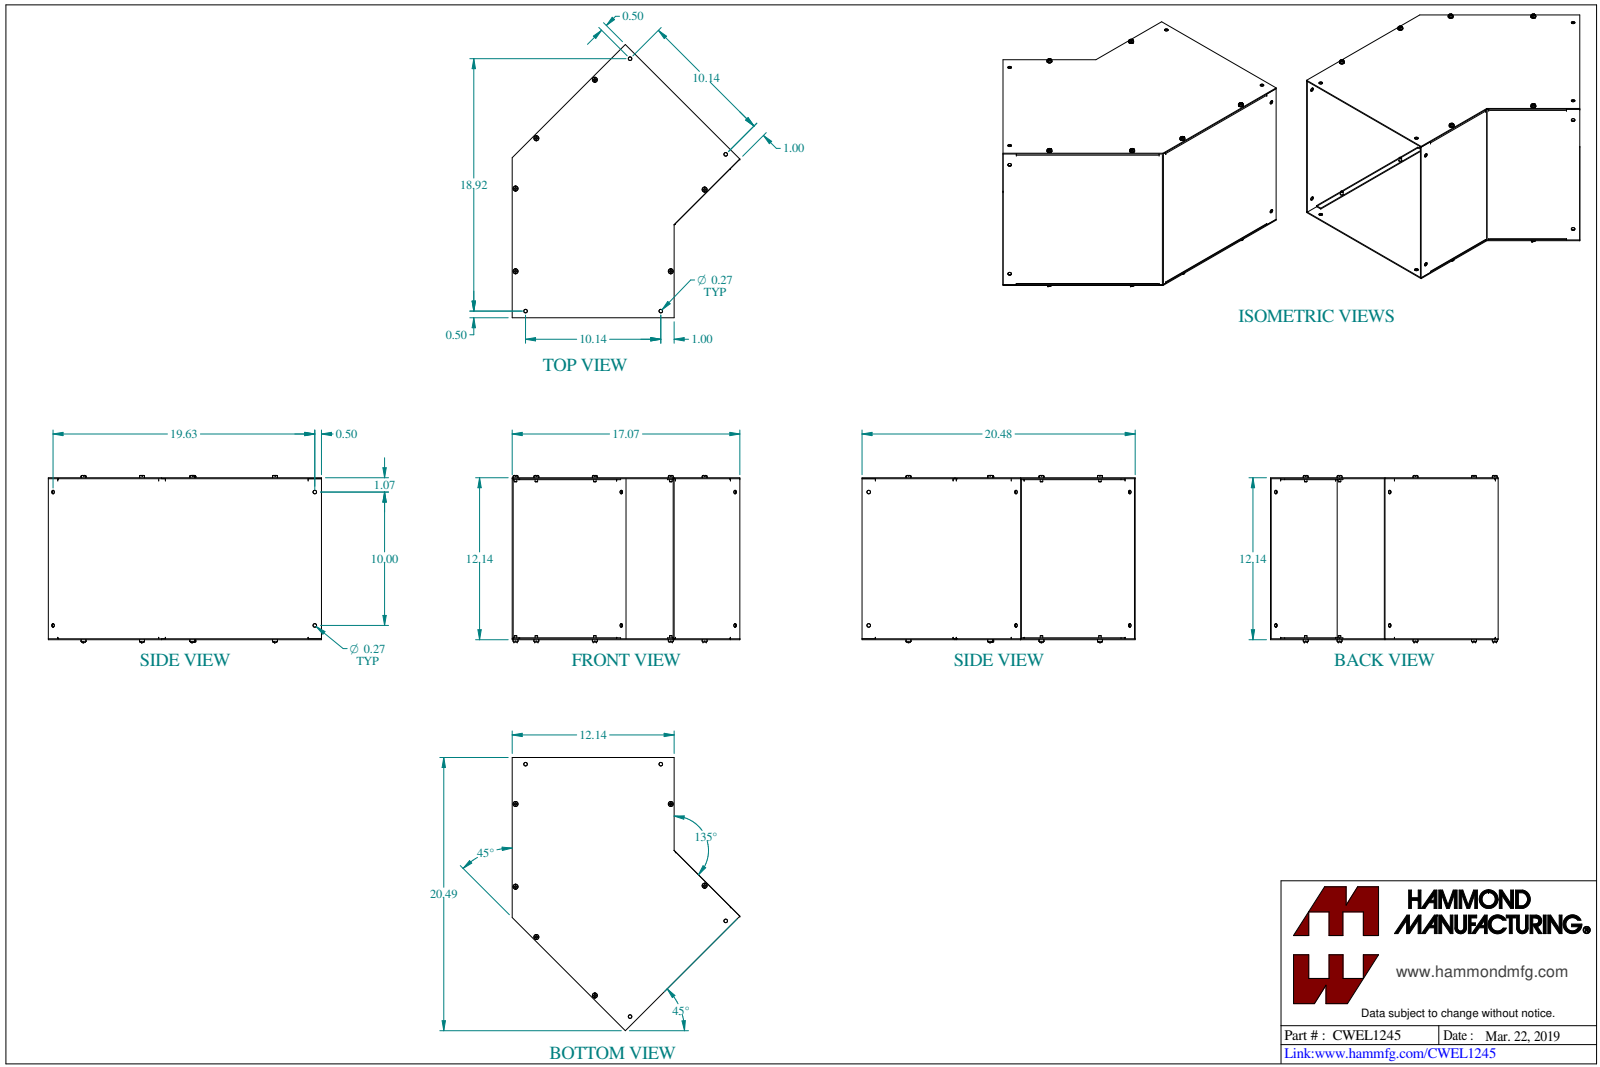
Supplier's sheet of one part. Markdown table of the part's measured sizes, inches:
| quantity | value |
| --- | --- |
| part name | CWEL1245 |
| STEP written by | SolidWorks 2023 (CONFIG_CONTROL_DESIGN) |
| units | inches |
| bodies | 16 solids, 536 faces (316 planar, 148 cylindrical, 72 other) |
| overall size | 20.485 × 17.072 × 12.494 |
| volume | 68 in³ |
| surface area | 1 909 in² |
| round holes (diameter × count) | 0.266 × 10, 0.17 × 6, 0.25 × 6 |
| round bosses / shafts (diameter × count) | 0.19 × 6, 0.375 × 4, 0.375 × 2 |
| partial cylindrical surfaces (radius × count) | 0.036 × 10, 0.108 × 10 |
| main face-to-face distances | 0.072, 12.072, 12, 12.144, 12.07, 12.142, 11.998, 0.144, 11.928, 11.856 |
| hole center spacings | 10, 11.296, 15.969, 3.078, 3.078, 6.203, 9.218, 9.685 |
